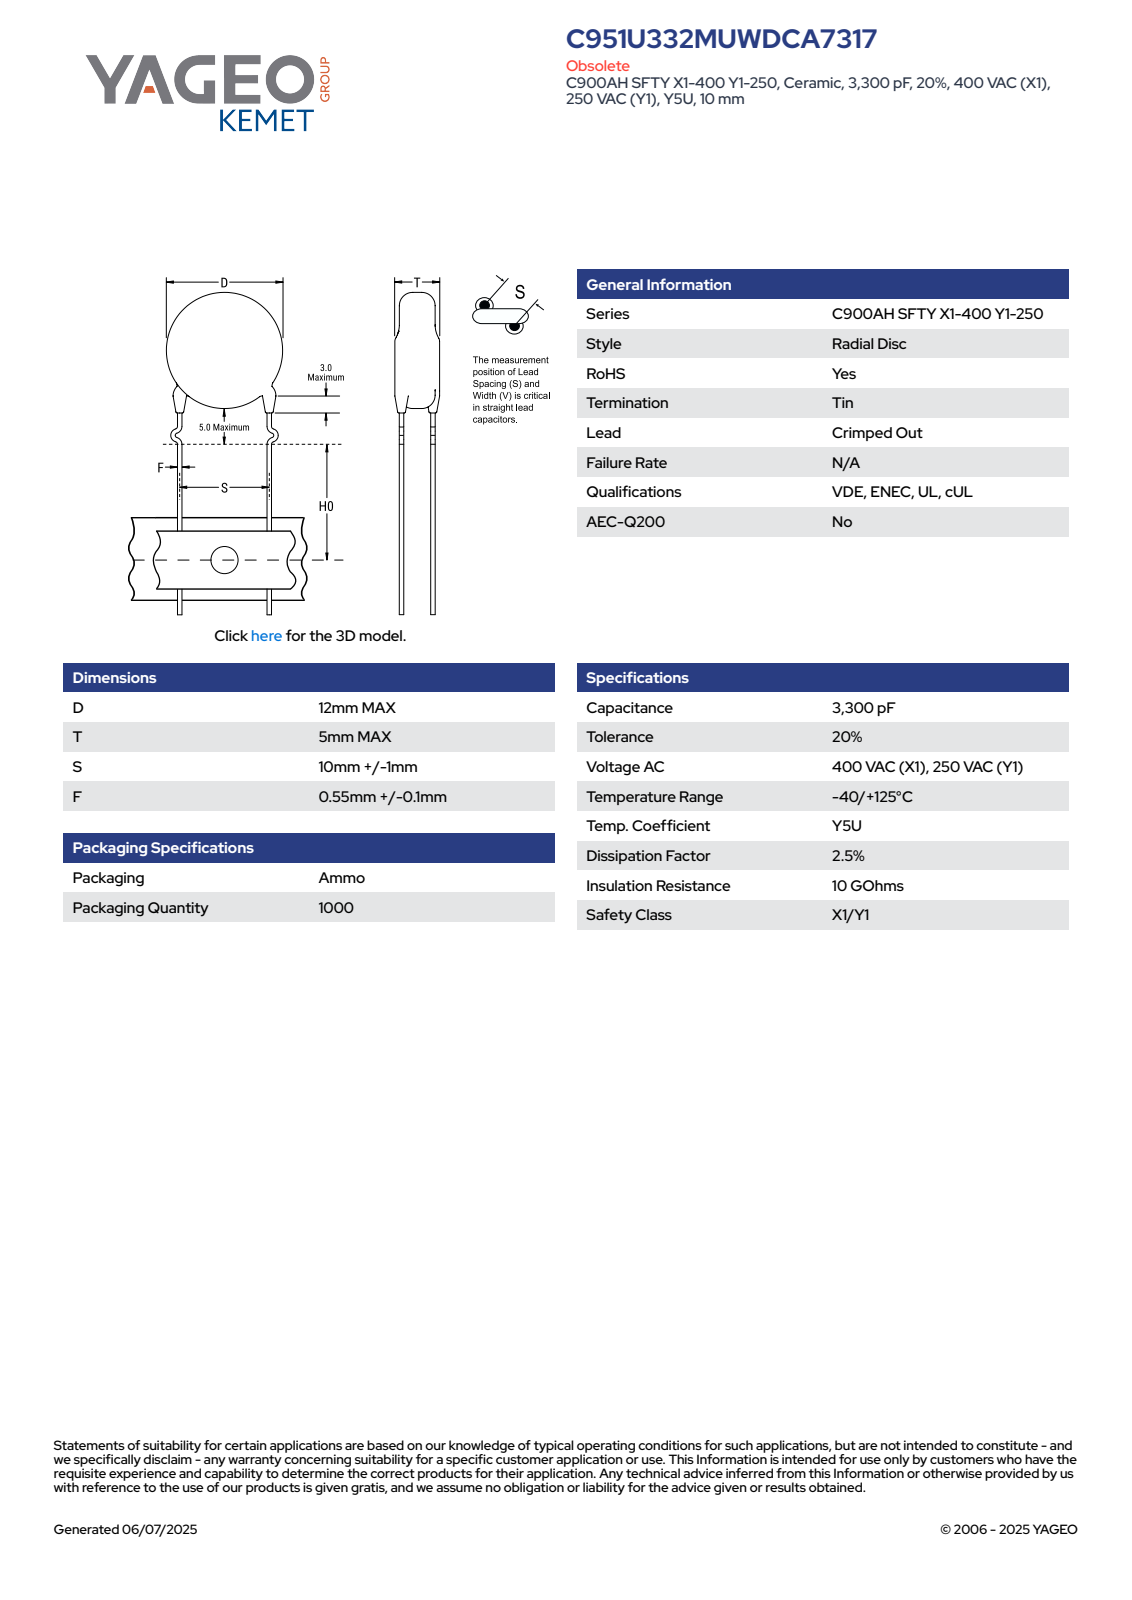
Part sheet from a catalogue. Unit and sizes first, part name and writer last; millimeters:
Units: millimetres
Overall size (bounding box): 37 × 14.98 × 5
Round bosses / shafts (diameter × count): ⌀1.2 ×2, ⌀12 ×1
Main face-to-face distances: 5, 6.63, 5.39, 1.24, 0.34, 5.1, 0.46, 1, 0.45, 2.58
Volume: 574 mm³ · Surface area: 521 mm²
Bodies: 4 solids, 85 faces (63 planar, 6 cylindrical, 16 other)
Part name (STEP PRODUCT): CCD_KCOC900_D12T5S10LL20F0.55
STEP written by: SolidWorks 2014 (AUTOMOTIVE_DESIGN)
